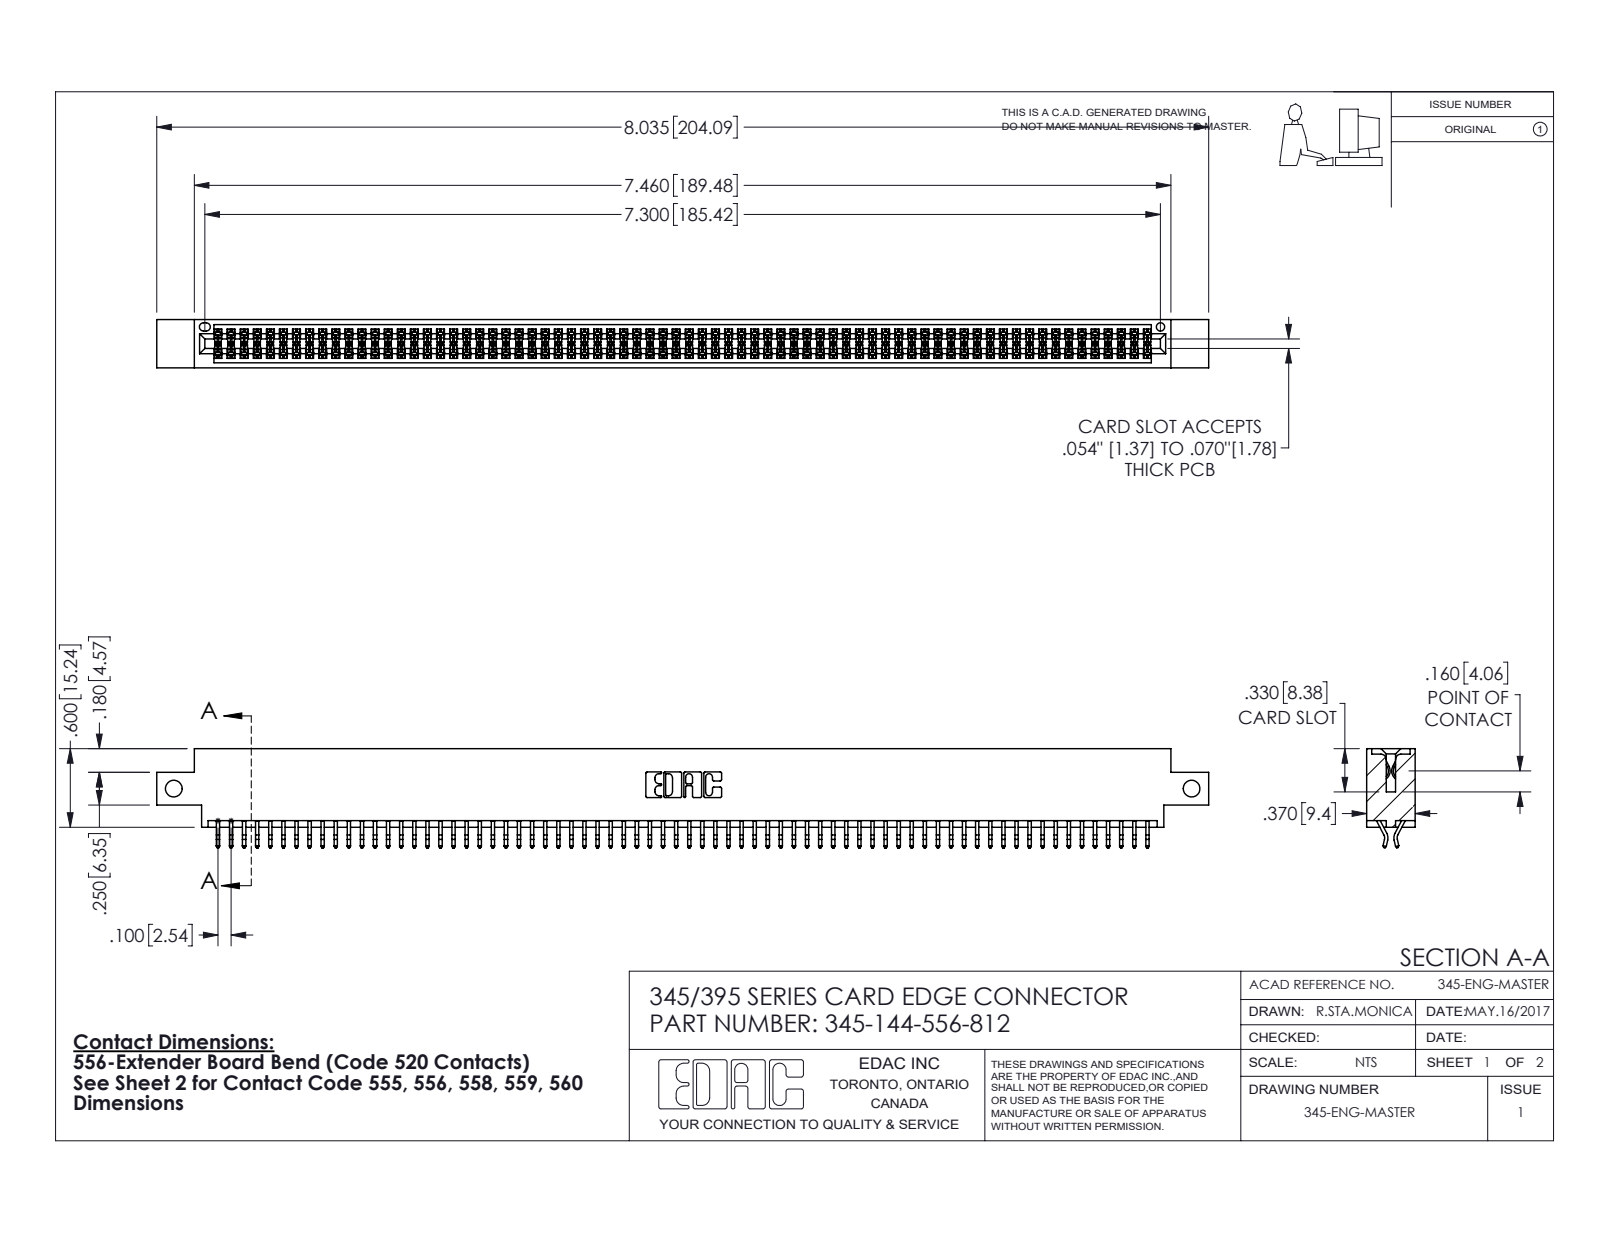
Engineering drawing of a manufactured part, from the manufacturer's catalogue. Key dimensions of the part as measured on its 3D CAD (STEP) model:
Part name (STEP PRODUCT): 345-292-001_556 Tail; 345-144-556-812; 345 Part_0.170 Offset - Side Mount
STEP written by: SolidWorks 2016 (CONFIG_CONTROL_DESIGN)
Units: inches
Bodies: 145 solids, 8194 faces (5412 planar, 2782 cylindrical, 0 other)
Overall size (bounding box): 8.035 × 0.757 × 0.37
Volume: 1.214 in³ · Surface area: 46.31 in²
Round holes (diameter × count): ⌀0.128 ×2, ⌀0.064 ×1
Partial cylindrical surfaces — rounded edges, fillets, slot ends (radius × count): R0.006 ×216, R0.01 ×22, R0.007 ×6, R0.031 ×6, R0.026 ×3, R0.01 ×2, R0.014 ×2, R0.019 ×2
Main face-to-face distances: 0.298, 0.072, 0.37, 0.2, 0.025, 0.098, 0.272, 0.225, 0.175, 0.149
Hole centre spacings: 7.775
